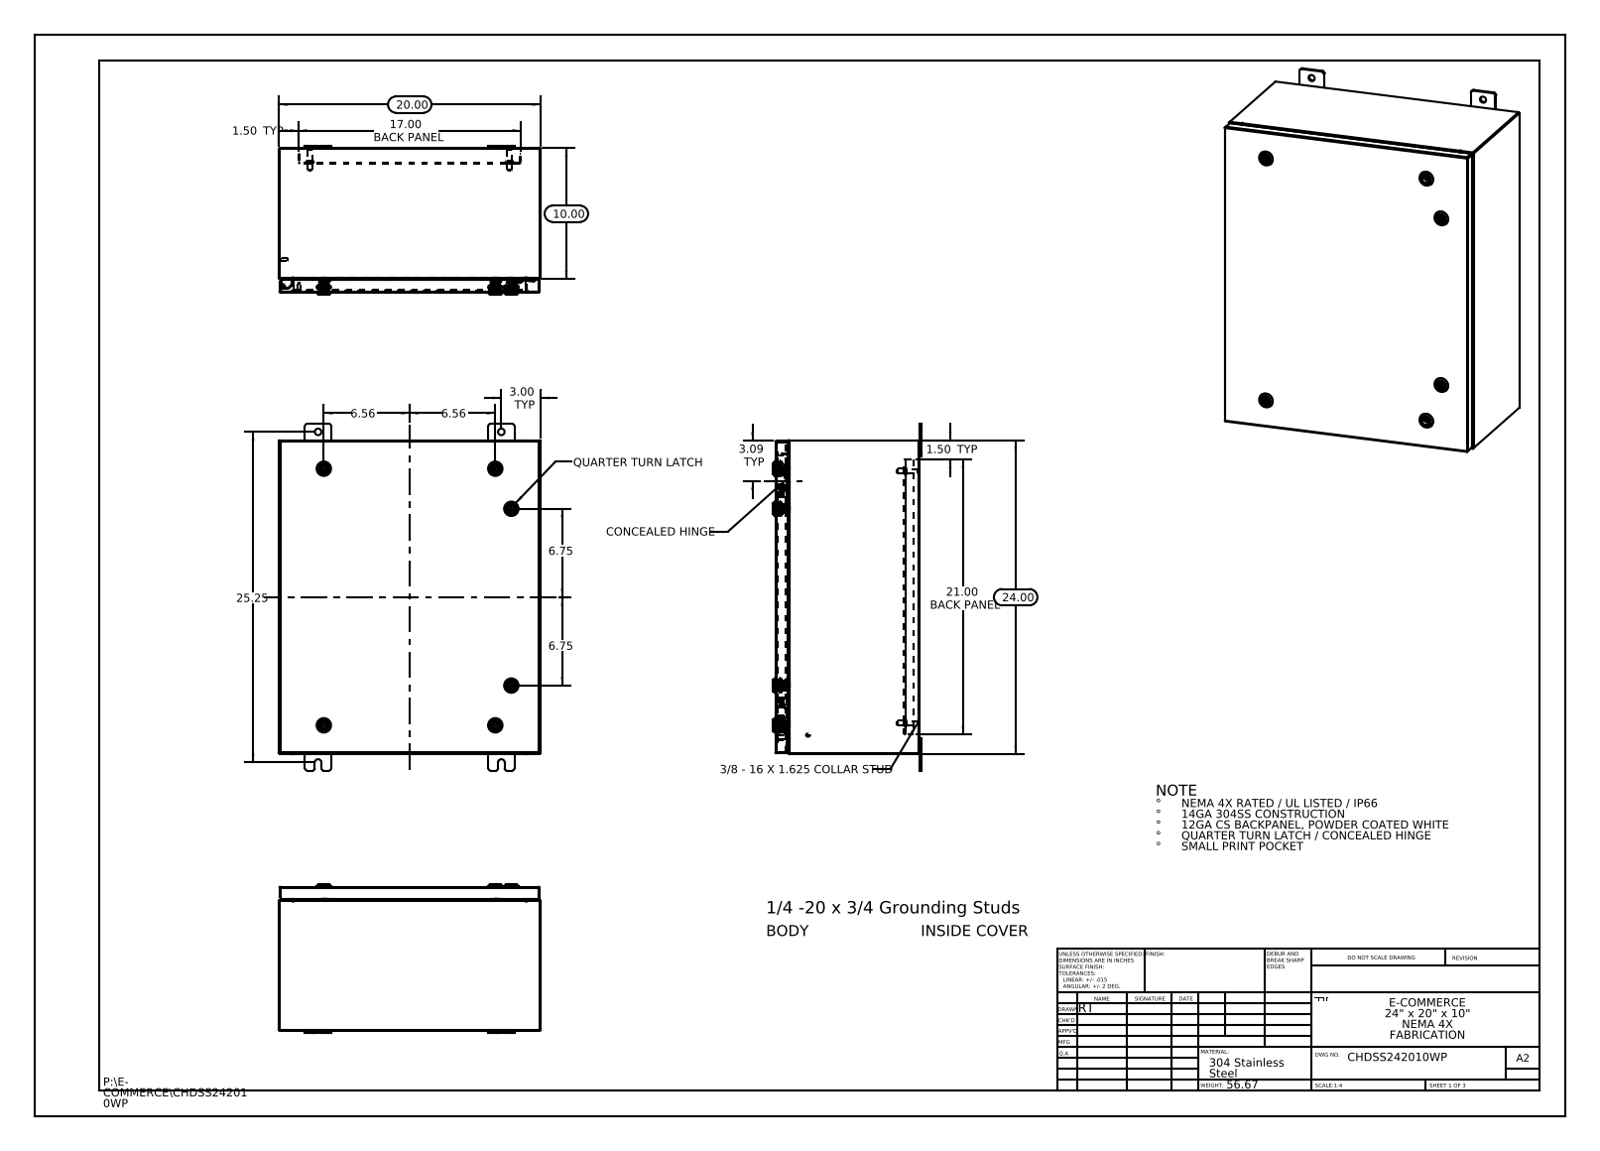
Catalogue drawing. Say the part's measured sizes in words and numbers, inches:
The part is named "Screw-221320-IB-Industrilas_Screw-221320-IB-Industrilas; CHDSS242010WP Backpanel; Concealed Hinge enclosure side; CHDSS242010WP Mounting Feet (+8 more)". Its 3-D file was written by "SolidWorks 2013 (CONFIG_CONTROL_DESIGN)". It is 55 solids with 5420 faces: 1592 planar, 1692 cylindrical and 2136 other. Overall it measures 26.5 by 20 by 11.356 inches. Its volume is 202.2 cubic inches and its surface area 5 077 square inches. Round holes: 8 of diameter 0.5, 6 of diameter 0.197, 6 of diameter 0.394, 6 of diameter 0.4, 6 of diameter 0.63, 6 of diameter 0.787, 4 of diameter 0.136, 1 of diameter 0.211. Round bosses or shafts: 8 of diameter 0.236, 6 of diameter 1.102, 6 of diameter 0.78, 6 of diameter 0.626, 6 of diameter 0.61, 6 of diameter 0.531, 6 of diameter 0.392, 6 of diameter 0.114. Partial cylindrical surfaces (rounded edges, fillets, slot ends): 198 of radius 0.006, 198 of radius 0.118, 72 of radius 0.028, 24 of radius 0.02, 24 of radius 0.19, 24 of radius 0.197, 20 of radius 0.013, 18 of radius 0.088. The main face-to-face distances are 0.075, 0.074, 19.925, 11.01, 10.935, 10.936, 10.861, 23.925, 0.104, 1. The hole center spacings are 0.688, 1.858, 2.878, 3.065, 13.1, 14, 15.25, 15.655.
